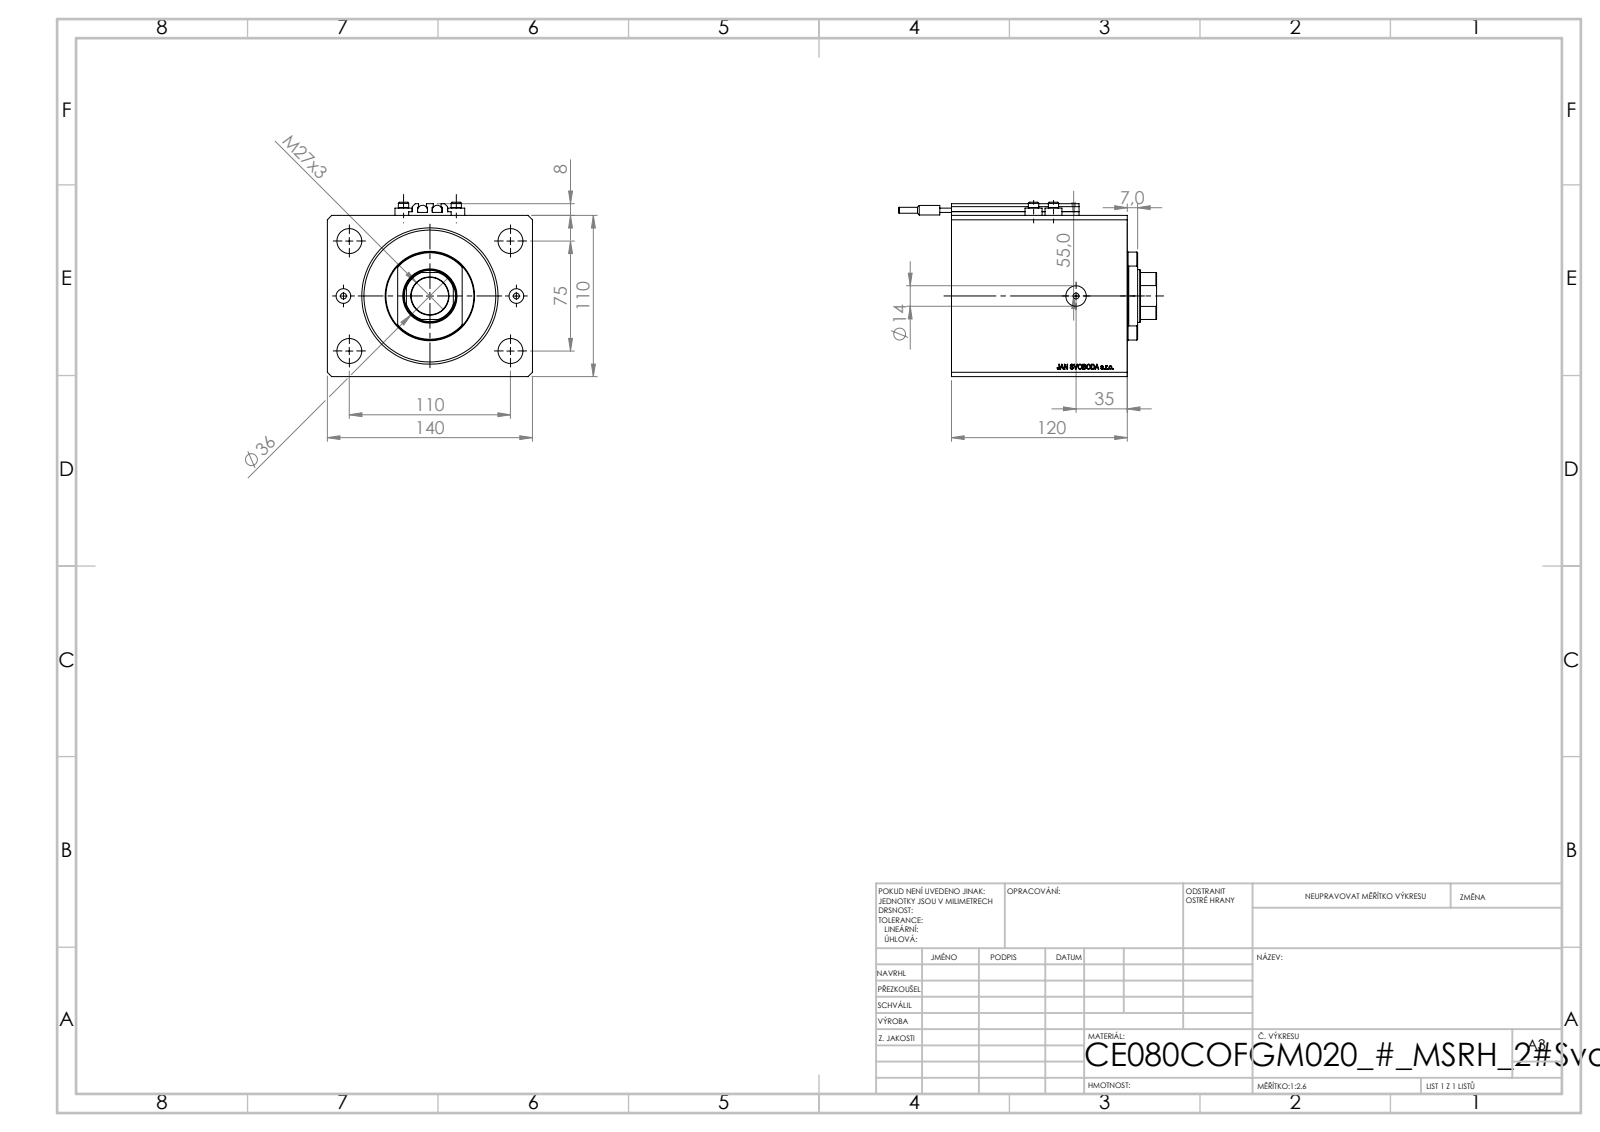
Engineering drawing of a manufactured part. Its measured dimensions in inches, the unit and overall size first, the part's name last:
Units: inches
Overall size (bounding box): 6.929 × 5.512 × 4.685
Round holes (diameter × count): ⌀0.157 ×8, ⌀0.669 ×4, ⌀0.394 ×2, ⌀0.551 ×2, ⌀1.004 ×1, ⌀1.417 ×1, ⌀3.15 ×1, ⌀3.661 ×1
Round bosses / shafts (diameter × count): ⌀0.457 ×4, ⌀0.276 ×4, ⌀0.268 ×2, ⌀0.256 ×2, ⌀0.157 ×2, ⌀2.362 ×1
Partial cylindrical surfaces — rounded edges, fillets, slot ends (radius × count): R0.008 ×10, R0.689 ×1
Main face-to-face distances: 4.331, 5.512, 0.787, 4.724, 3.74, 0.984, 2.953, 3.937, 1.575, 3.15
Hole centre spacings: 1.485, 2.621, 4.725, 0.535, 1.417, 1.515, 2.323, 2.953
Volume: 102.2 in³ · Surface area: 326 in²
Bodies: 10 solids, 1086 faces (536 planar, 98 cylindrical, 452 other)
Part name (STEP PRODUCT): SWITCH_V250CE; ALLEN BOLT V250CE; V250CE_C_Body; V250CE_C_VCP (+1 more)
STEP written by: SolidWorks 2019 (CONFIG_CONTROL_DESIGN)
